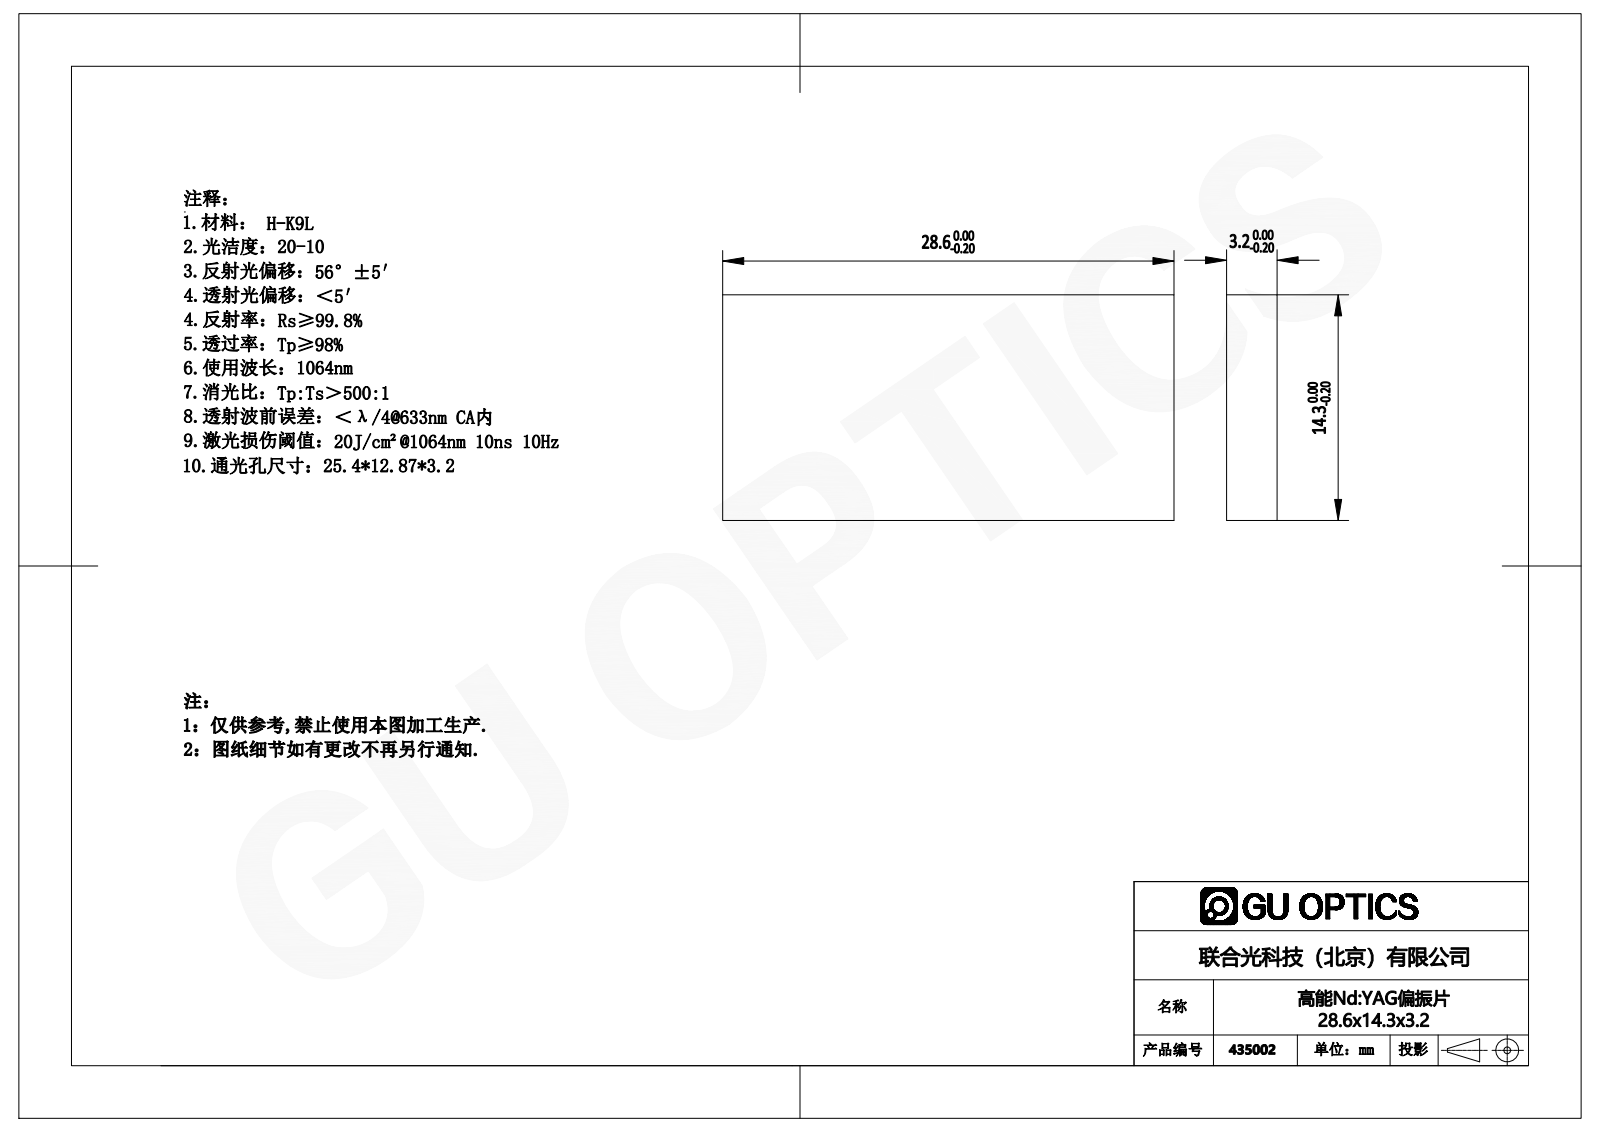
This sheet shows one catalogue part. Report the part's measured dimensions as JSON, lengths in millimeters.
{"part_name": "435002", "step_written_by": "SolidWorks 2016 (AUTOMOTIVE_DESIGN)", "units": "millimeters", "bodies": {"solids": 1, "faces": 7, "planar": 7, "cylindrical": 0, "other": 0}, "overall_size": [28.6, 14.47, 3.2], "volume_mm3": 1316, "surface_area_mm2": 1097, "face_to_face_distances": [3.2, 28.6]}
